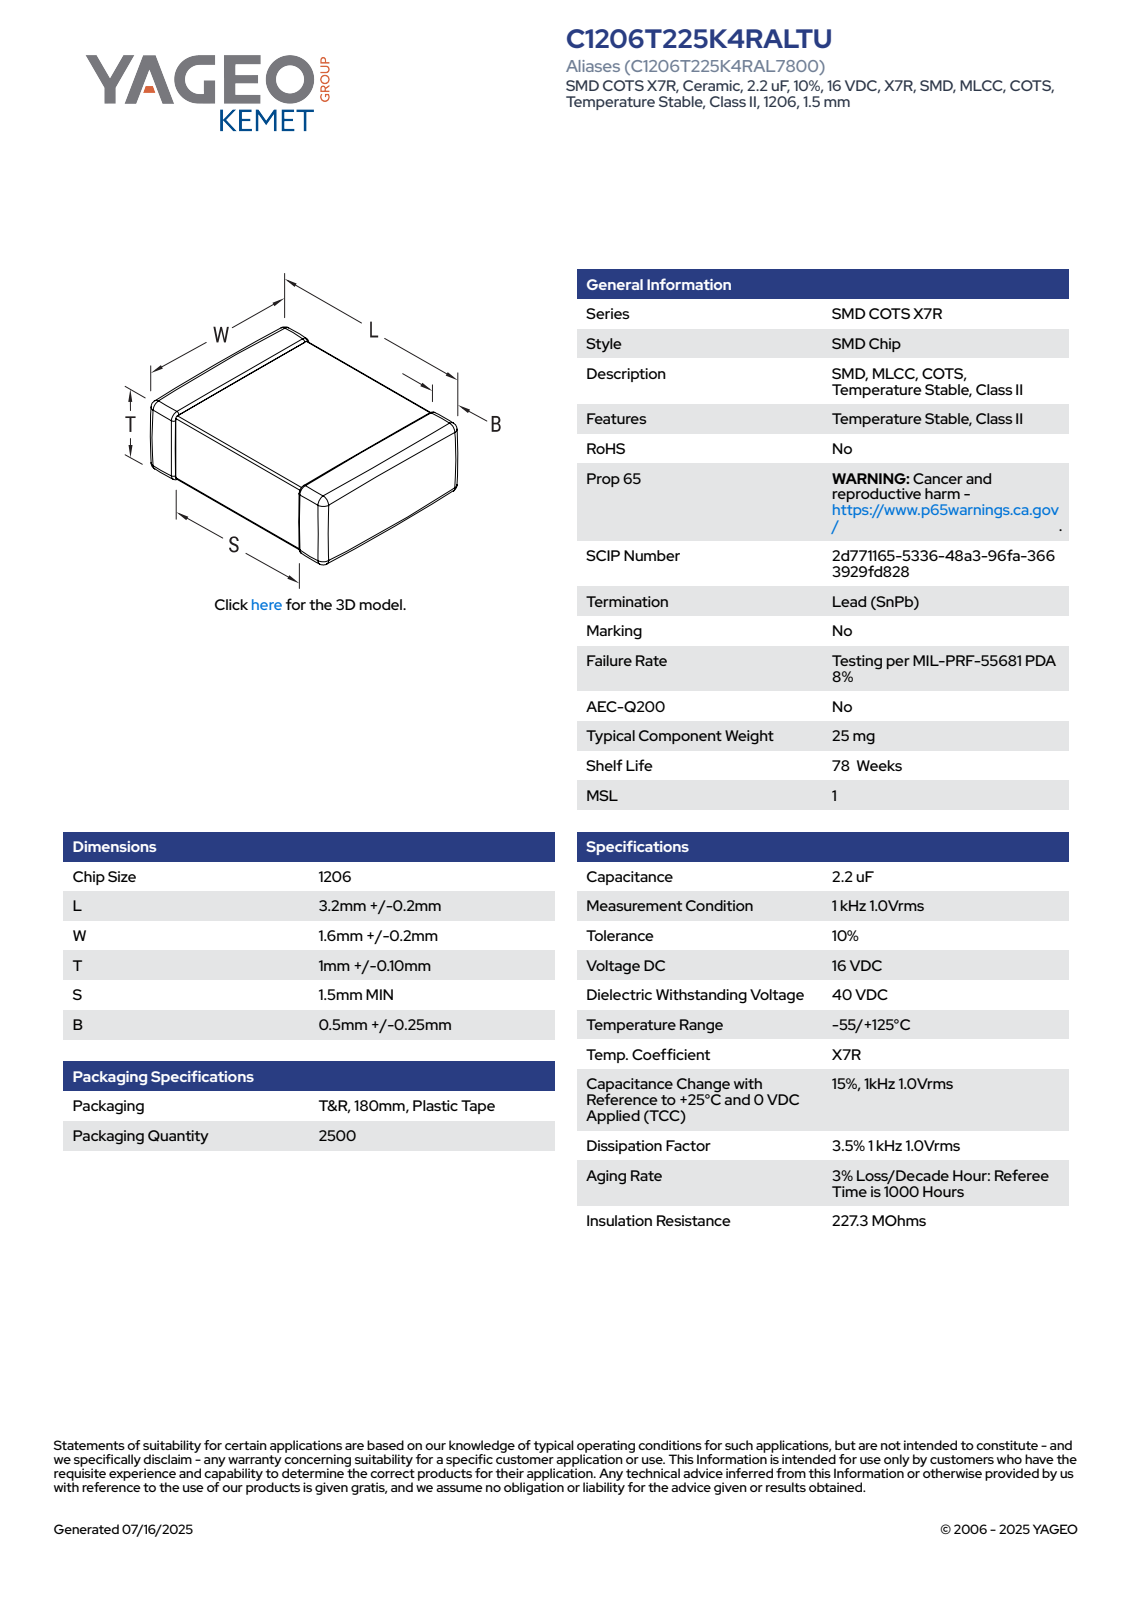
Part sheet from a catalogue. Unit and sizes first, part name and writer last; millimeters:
Units: millimetres
Overall size (bounding box): 3.4 × 1.8 × 1.1
Main face-to-face distances: 1.02, 1.06, 1.72, 3.4, 1.76, 1.1, 1.8, 1.03, 1.07, 0.72
Volume: 6 mm³ · Surface area: 23 mm²
Bodies: 4 solids, 121 faces (71 planar, 34 cylindrical, 16 other)
Part name (STEP PRODUCT): CCS_STDNOS_1206_L3.4W1.8T1.1B0.5
STEP written by: SolidWorks 2014 (AUTOMOTIVE_DESIGN)
